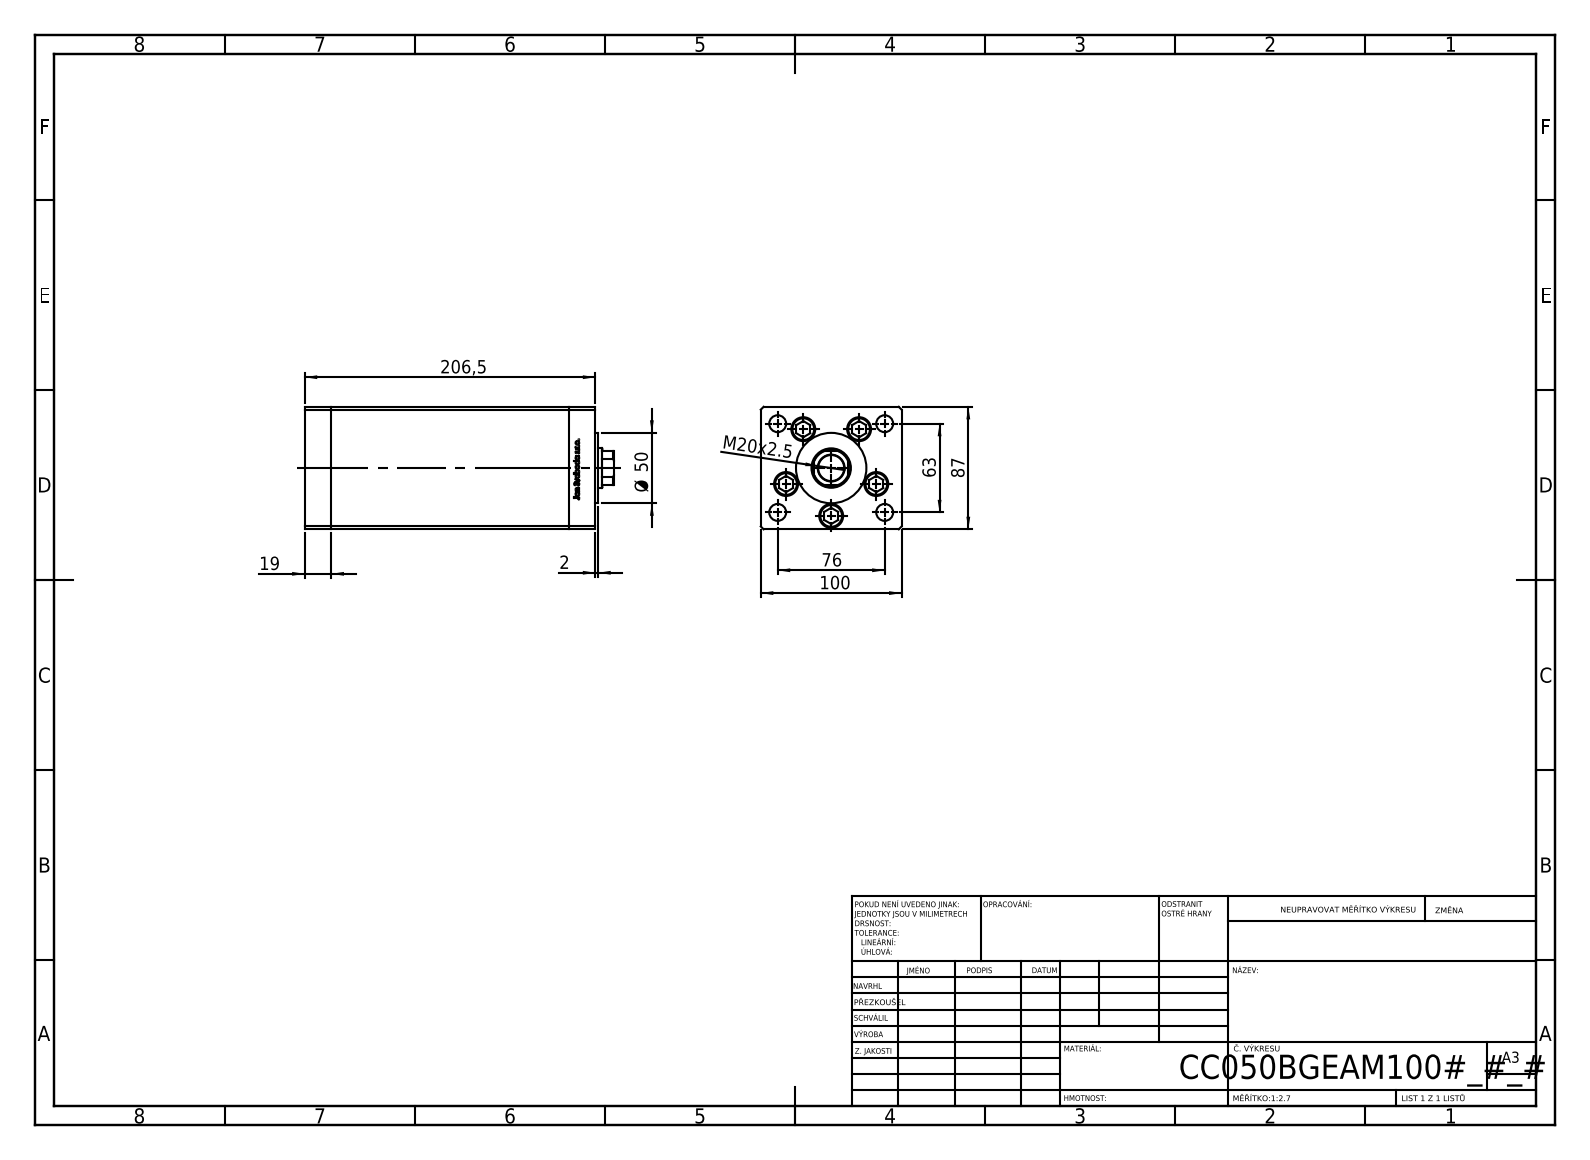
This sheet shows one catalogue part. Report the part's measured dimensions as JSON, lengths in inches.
{"part_name": "V220C BACK_B; V220C_B MIDDLE; ALLEN BOLT; V220C_VC_B (+1 more)", "step_written_by": "SolidWorks 2019 (CONFIG_CONTROL_DESIGN)", "units": "inches", "bodies": {"solids": 14, "faces": 1185, "planar": 464, "cylindrical": 147, "other": 574}, "overall_size": [8.642, 3.937, 3.425], "volume_in3": 96.11, "surface_area_in2": 338.1, "round_holes": [[0.531, 7], [0.669, 5], [0.472, 4], [0.079, 2], [0.518, 2], [0.728, 1], [1.102, 1]], "round_bosses_or_shafts": [[0.315, 5], [0.669, 2], [1.969, 1]], "partial_cylinders_radius": [[0.037, 2], [0.531, 1]], "face_to_face_distances": [3.937, 3.425, 0.748, 6.634, 7.382, 1.348, 8.13, 0.6, 6.033, 6.781], "hole_center_spacings": [1.339, 0.732, 1.561, 1.943, 2.281, 0.828, 1.499, 1.546]}
